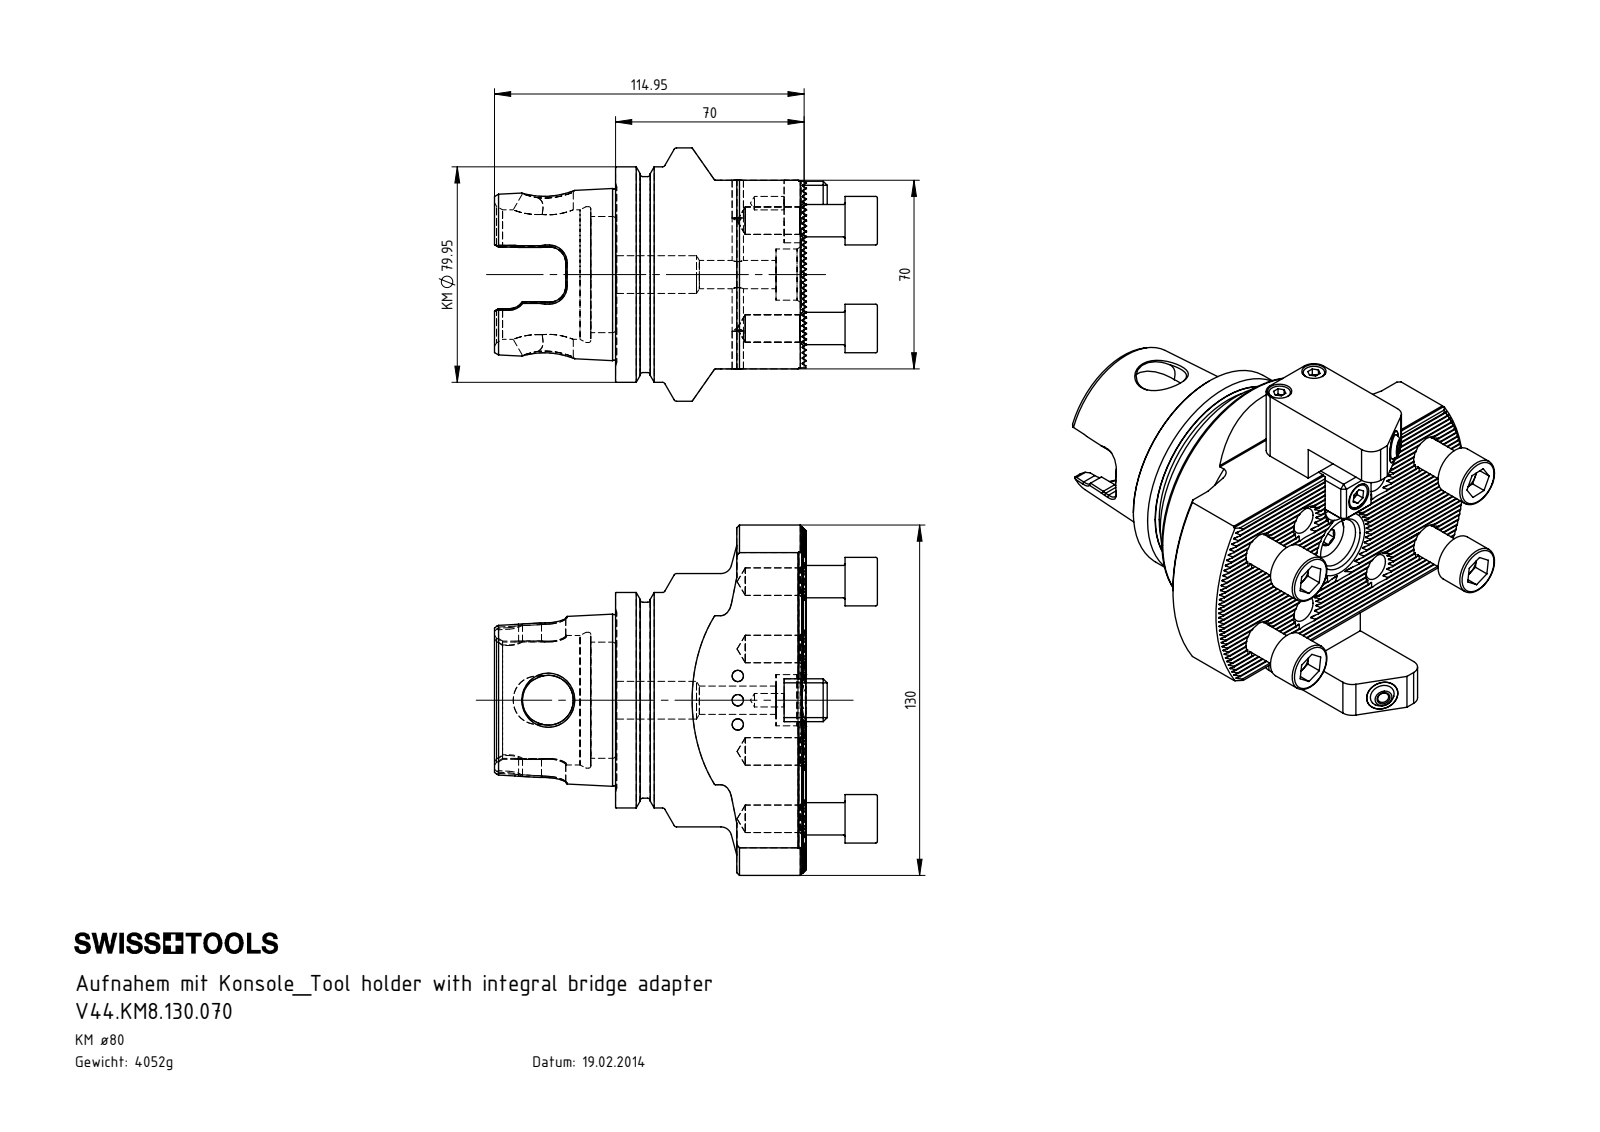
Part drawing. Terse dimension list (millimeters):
name: ISO 4762 - M6 x 16; KM8-Ko1.K21.070_D; ISO 4762 - M12 x 25; Ko1-ER1.001.016_A (+2 more)
written by: SolidWorks 2017 (AUTOMOTIVE_DESIGN)
unit: mm
bodies: 8 solids, 792 faces (491 planar, 167 cylindrical, 134 other)
size: 142.14 × 130 × 94
volume: 515 635 mm³; area: 79 930 mm²
holes: 8× ⌀10.2, 3× ⌀4.2, 2× ⌀10.5, 1× ⌀5, 1× ⌀6.5, 1× ⌀7.24, 1× ⌀14, 1× ⌀19, 1× ⌀43.1, 1× ⌀48.05, 1× ⌀50.4
bosses: 5× ⌀12, 4× ⌀18, 1× ⌀94, 1× ⌀79.95, 1× ⌀72.7, 1× ⌀17, 1× ⌀10, 1× ⌀6
rounds: 34× R0.14, 6× R6, 2× R0.5, 2× R9.04, 1× R7.95, 1× R9.25, 1× R65
face distances: 1.73, 70, 17.32, 8.66, 3.46, 5.2, 6.93, 15.59, 19.05, 3.47
hole spacings: 25, 27.59, 40, 47.17, 48.33, 63, 74.63, 9
